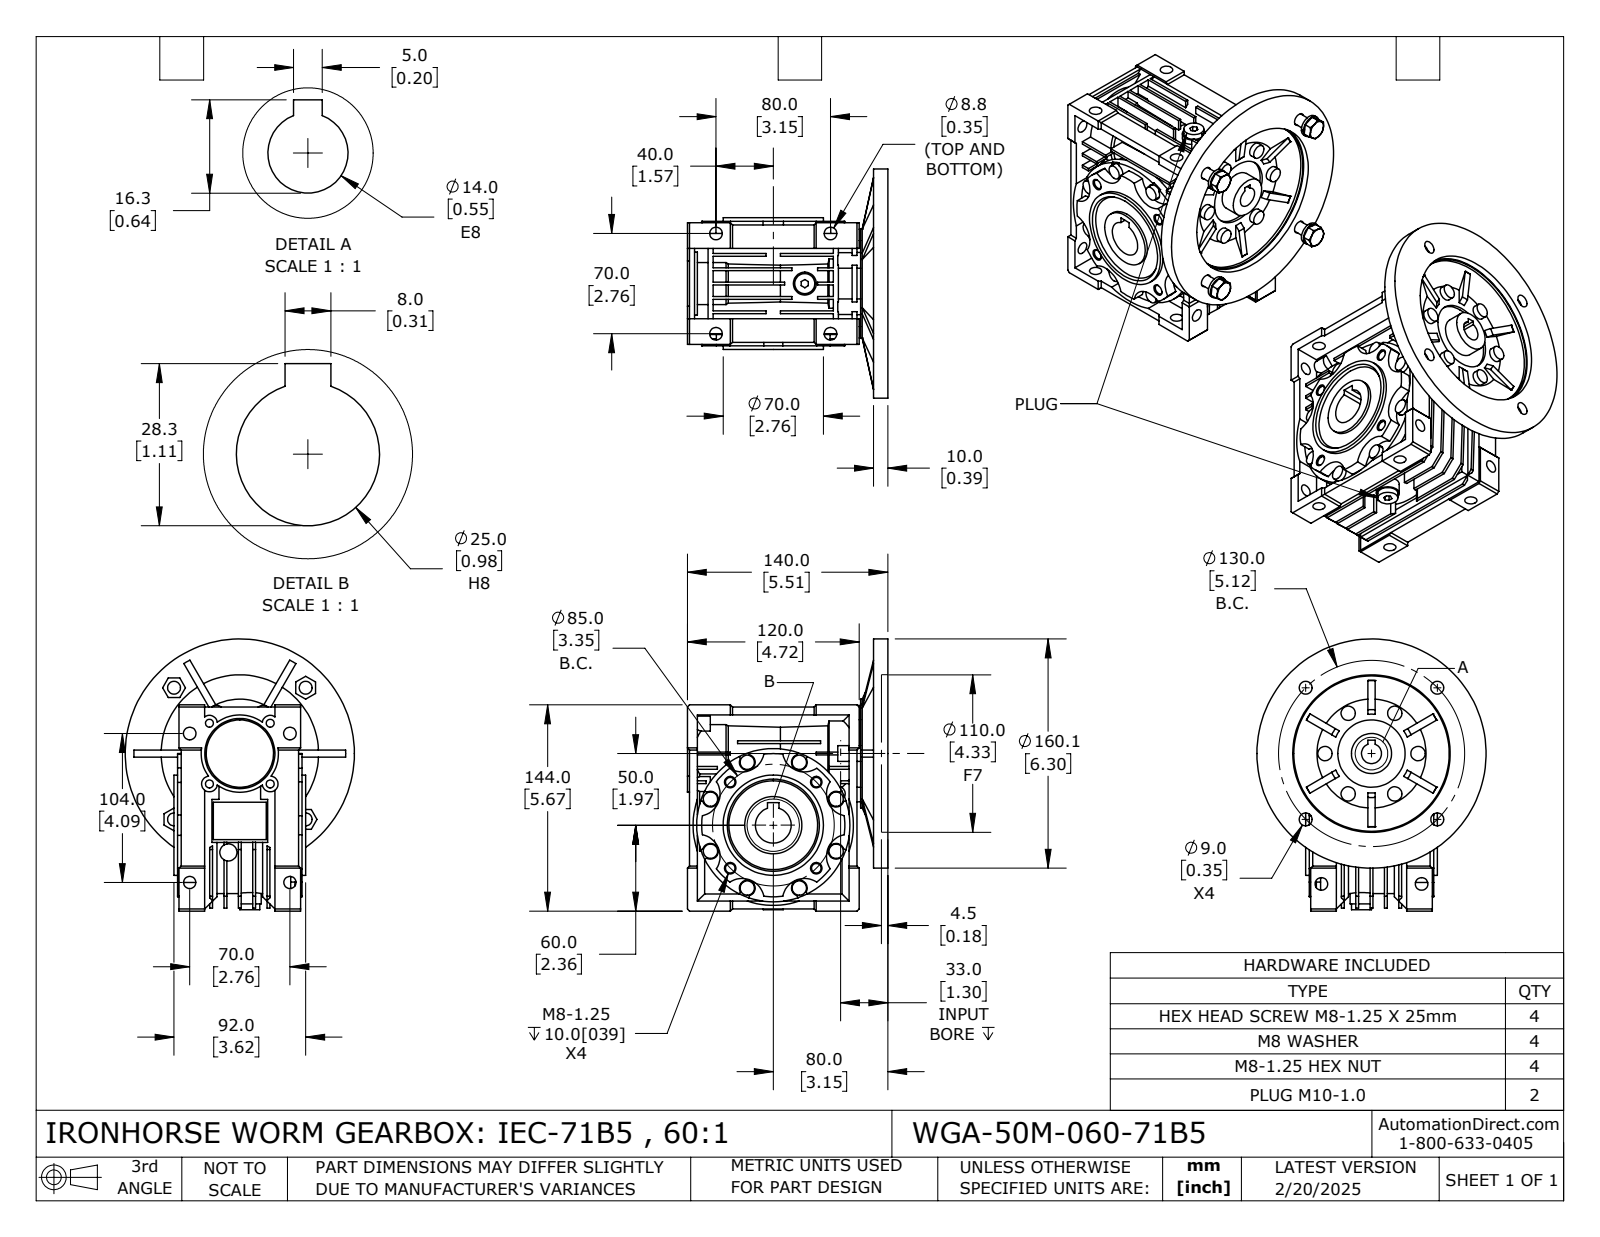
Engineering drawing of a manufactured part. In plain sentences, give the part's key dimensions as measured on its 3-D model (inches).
The part is named "WGA-50M-060-71B5". Its 3-D file was written by "SolidWorks 2024 (CONFIG_CONTROL_DESIGN)". It is 7 solids with 1007 faces: 577 planar, 316 cylindrical and 114 other. Overall it measures 7.481 by 6.302 by 5.512 inches. Its volume is 69.93 cubic inches and its surface area 397.8 square inches. Round holes: 8 of diameter 0.346, 6 of diameter 0.335, 6 of diameter 0.354, 4 of diameter 0.219, 2 of diameter 0.262, 2 of diameter 0.262, 1 of diameter 0.551, 1 of diameter 0.591, 1 of diameter 0.984, 1 of diameter 1.102, 1 of diameter 1.339, 1 of diameter 1.575. Round bosses or shafts: 14 of diameter 0.394, 2 of diameter 0.63, 2 of diameter 0.551, 2 of diameter 0.386, 2 of diameter 0.327, 1 of diameter 6.302, 1 of diameter 4.213, 1 of diameter 2.992. Partial cylindrical surfaces (rounded edges, fillets, slot ends): 18 of radius 0.217, 8 of radius 0.236, 8 of radius 0.591, 8 of radius 0.61, 1 of radius 0.817, 1 of radius 1.811, 1 of radius 1.878, 1 of radius 1.969. The main face-to-face distances are 0.394, 0.079, 0.276, 0.217, 0.315, 0.059, 0.787, 0.197, 2.165, 1.378. The hole center spacings are 2.818, 2.756, 1.181, 1.378, 1.67, 1.673, 2.366, 2.559.
